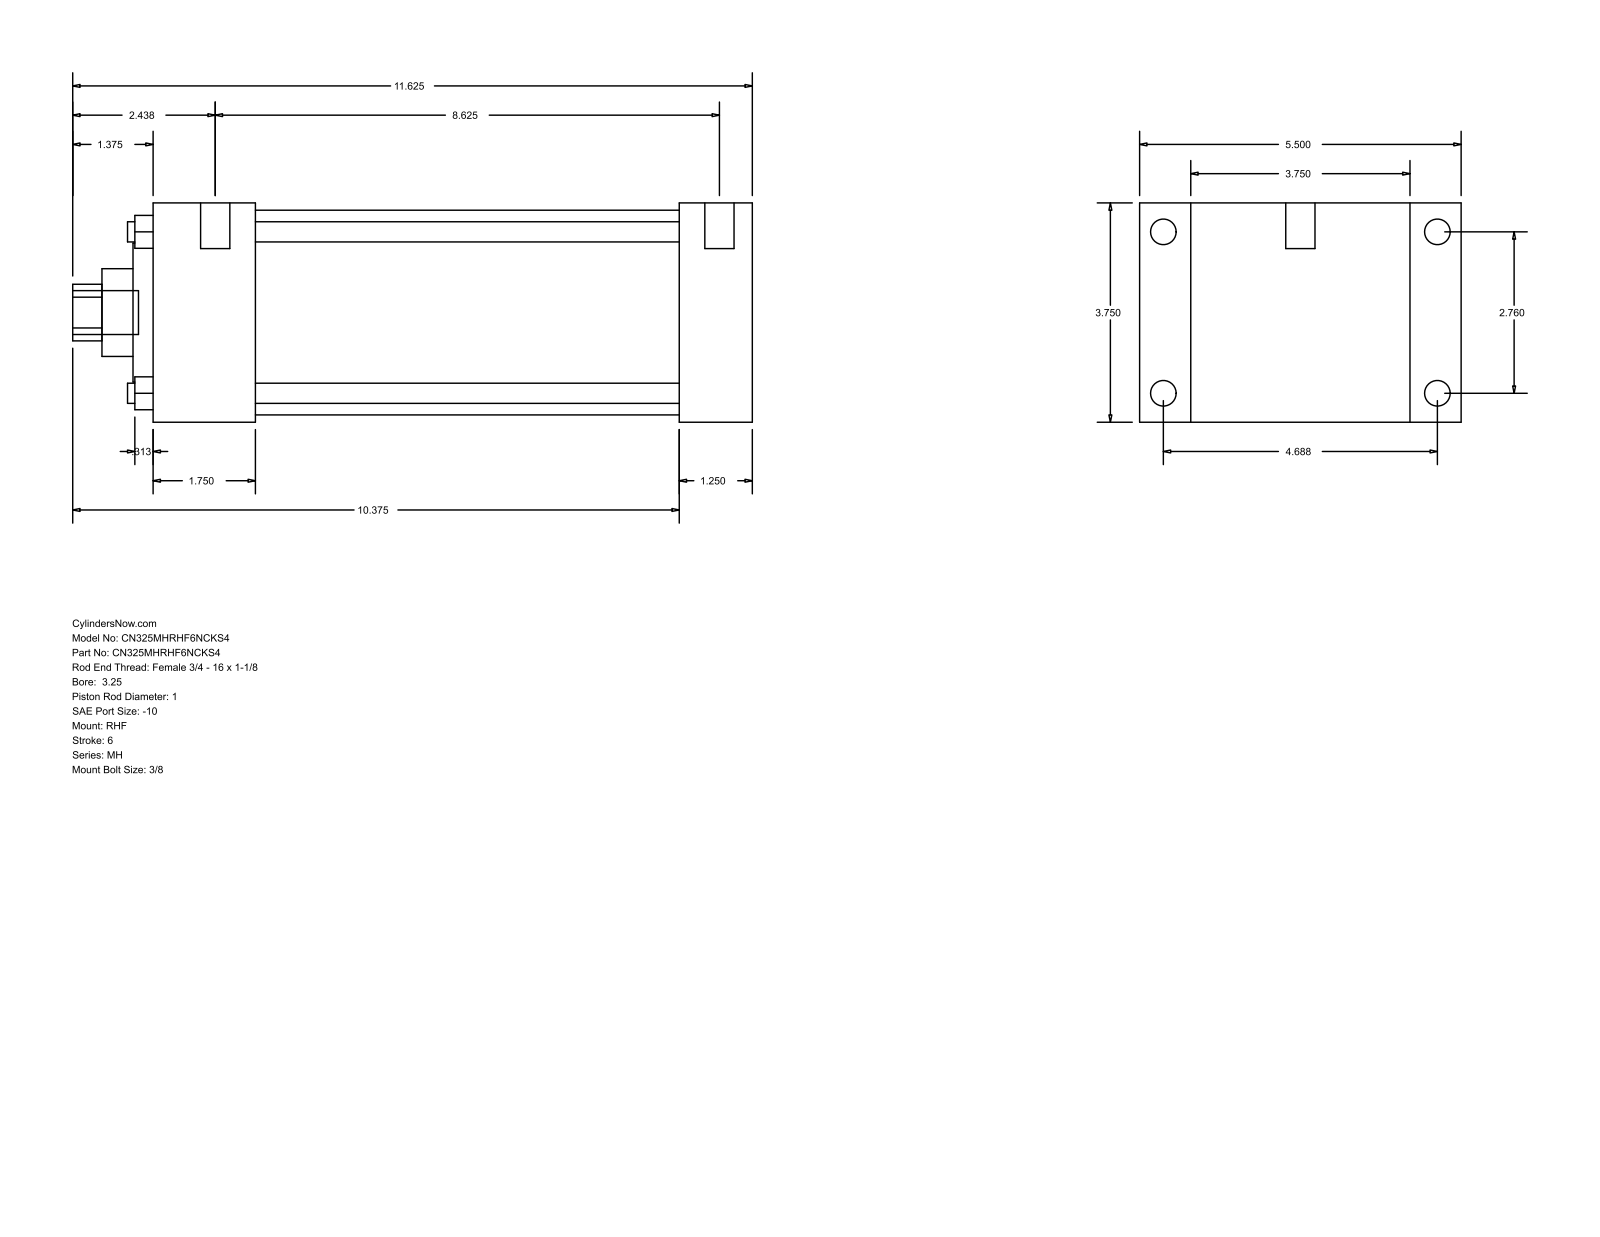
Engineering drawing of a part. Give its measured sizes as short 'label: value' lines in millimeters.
name: MH_RHF__0325_1
written by: GSSL Pune (CONFIG_CONTROL_DESIGN)
unit: mm
bodies: 0 solids, 90 faces (61 planar, 29 cylindrical, 0 other)
size: 295.27 × 139.7 × 95.25
holes: 4× ⌀8.76, 1× ⌀25.4, 1× ⌀38.1, 1× ⌀60.33, 1× ⌀88.9
bosses: 4× ⌀11.13, 4× ⌀5.56, 2× ⌀12.7, 1× ⌀19.05
rounds: 1× R12.29
face distances: 95.24, 31.75, 22.23, 117.47, 228.6, 260.35, 139.7, 44.46, 184.14, 215.89
hole spacings: 49.57, 70.1, 99.14
